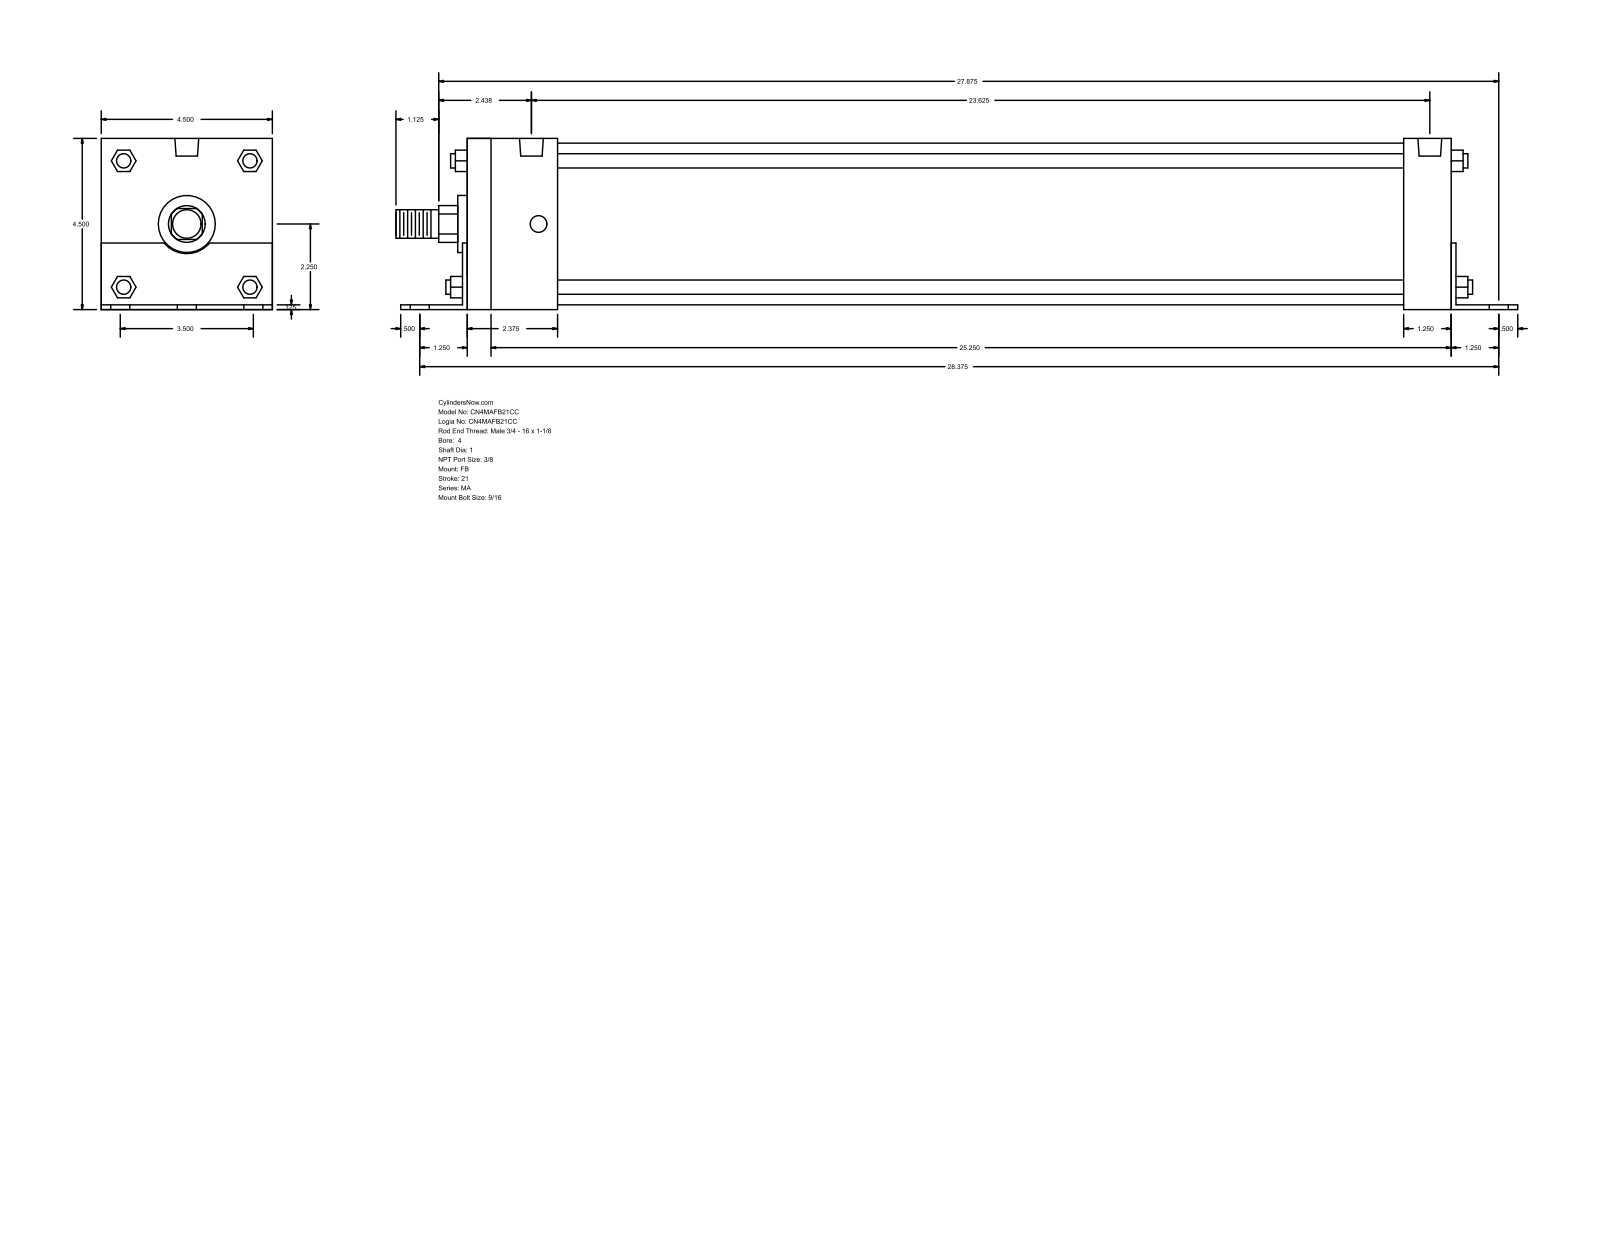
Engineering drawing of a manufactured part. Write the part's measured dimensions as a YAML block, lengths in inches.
part_name: "MA_FB__0400_1"
step_written_by: "GSSL Pune (CONFIG_CONTROL_DESIGN)"
units: inches
bodies: {solids: 0, faces: 140, planar: 105, cylindrical: 35, other: 0}
overall_size: [29.5, 4.502, 4.5]
round_holes:
  - {diameter: 0.563, count: 6}
  - {diameter: 0.437, count: 4}
  - {diameter: 0.627, count: 2}
round_bosses_or_shafts:
  - {diameter: 0.375, count: 4}
  - {diameter: 4.25, count: 1}
  - {diameter: 1.5, count: 1}
  - {diameter: 1, count: 1}
  - {diameter: 0.75, count: 1}
partial_cylinders:
  - {radius: 0.484, count: 1}
  - {radius: 0.78, count: 1}
face_to_face_distances: [4.5, 0.125, 4.502, 0.123, 4.377, 25.875, 0.125, 26.125, 26, 26]
hole_center_spacings: [1.75, 28.429, 28.375, 0.187, 2.519, 2.657, 3.419, 3.5]
